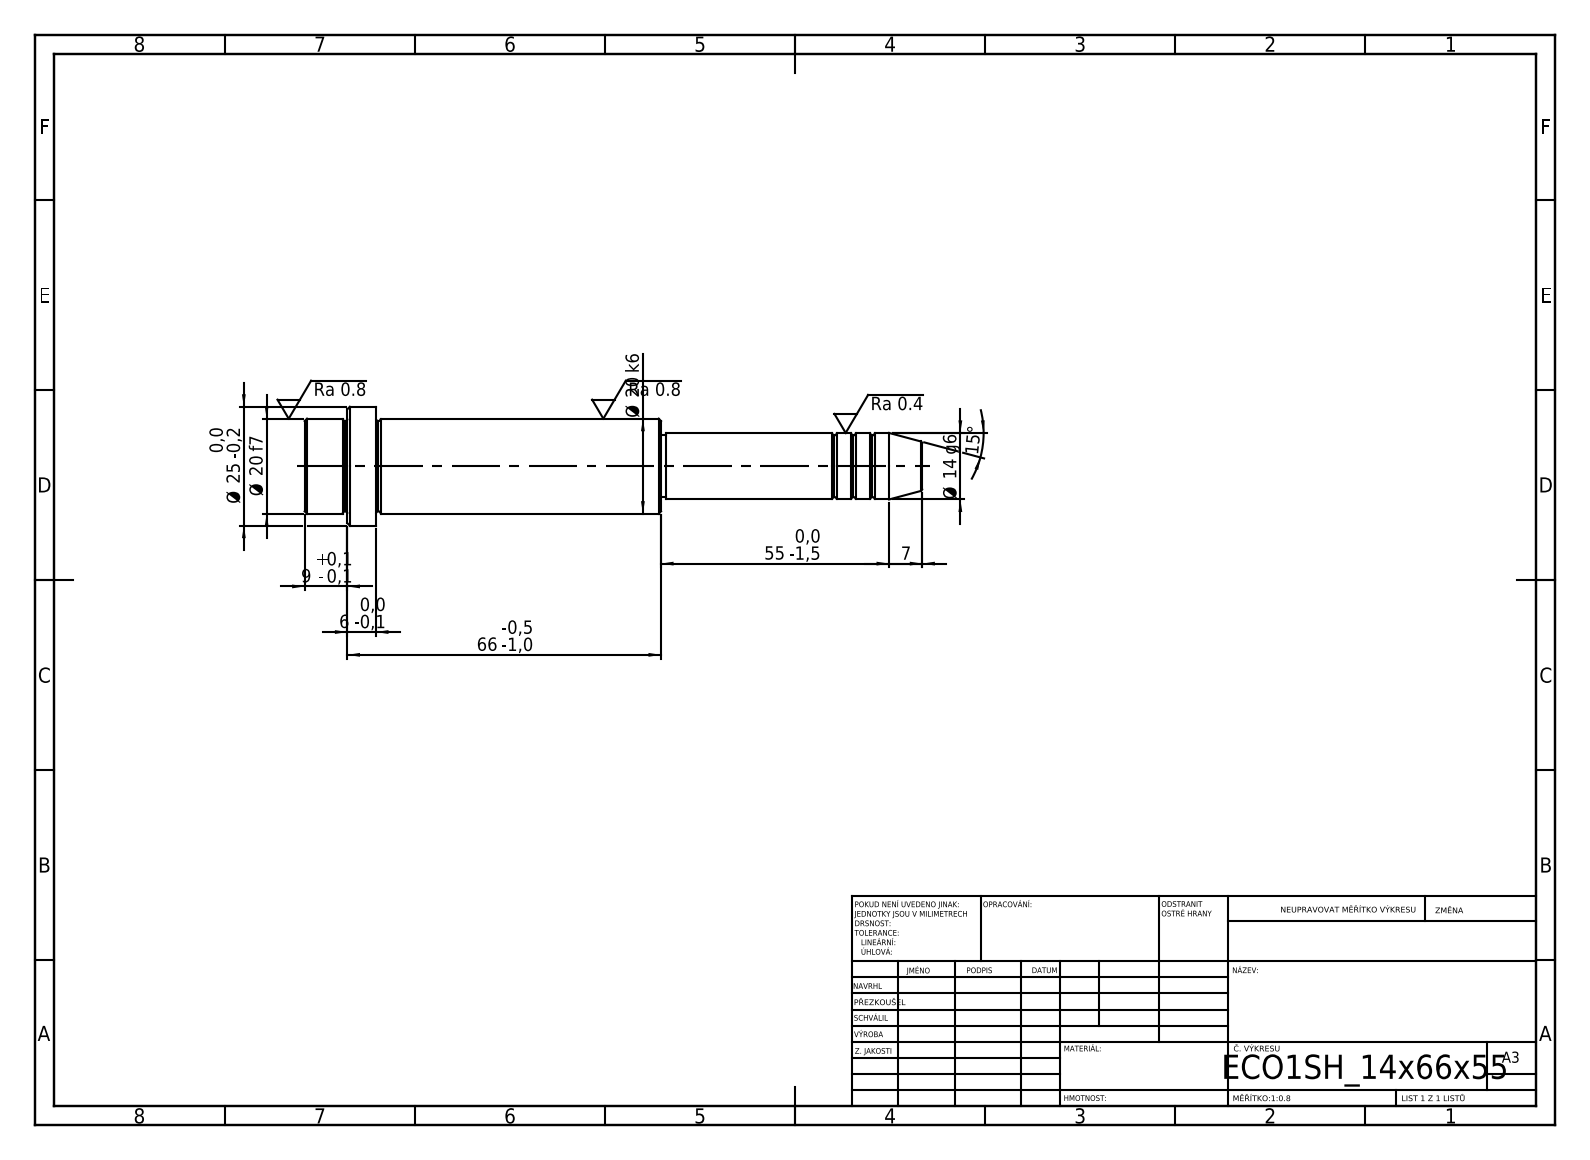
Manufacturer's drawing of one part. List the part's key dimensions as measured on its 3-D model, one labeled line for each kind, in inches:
STEP written by: SolidWorks 2019 (CONFIG_CONTROL_DESIGN)
Units: inches
Bodies: 1 solid, 52 faces (6 planar, 16 cylindrical, 30 other)
Overall size (bounding box): 5.118 × 0.984 × 0.984
Volume: 1.994 in³ · Surface area: 12.73 in²
Round bosses / shafts (diameter × count): ⌀0.984 ×1, ⌀0.787 ×1, ⌀0.551 ×1, ⌀0.512 ×1
Main face-to-face distances: 0.591, 2.362, 2.953, 2.598, 0.236, 0.354, 2.165, 4.528, 4.764, 5.118
